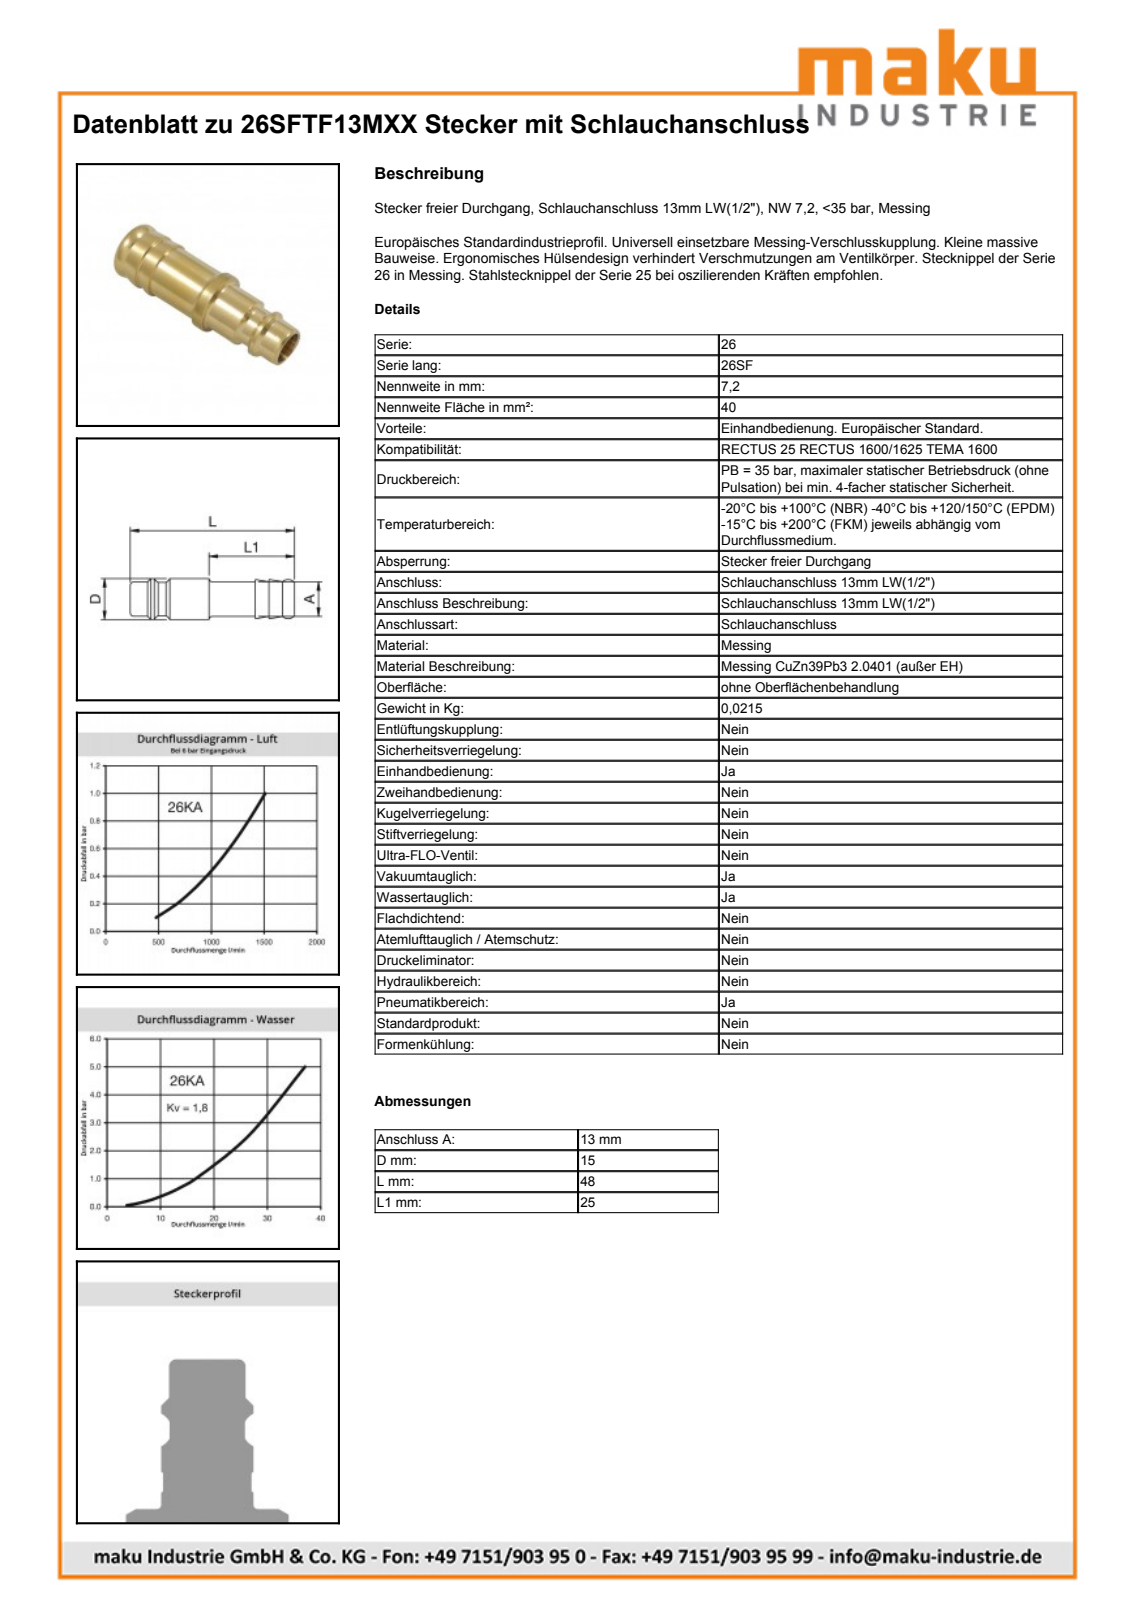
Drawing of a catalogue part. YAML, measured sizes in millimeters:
part_name: "D106814"
step_written_by: "Autodesk Inventor 2013 (AUTOMOTIVE_DESIGN)"
units: millimeters
bodies: {solids: 1, faces: 25, planar: 4, cylindrical: 8, other: 13}
overall_size: [48, 15, 15]
volume: 2553
surface_area: 3578
round_holes:
  - {diameter: 7.85, count: 1}
  - {diameter: 11, count: 1}
round_bosses_or_shafts:
  - {diameter: 15, count: 1}
  - {diameter: 13.1, count: 1}
  - {diameter: 12, count: 1}
  - {diameter: 10, count: 1}
  - {diameter: 9.75, count: 1}
face_to_face_distances: [28, 16.5, 11.5, 20, 36.5, 48]
